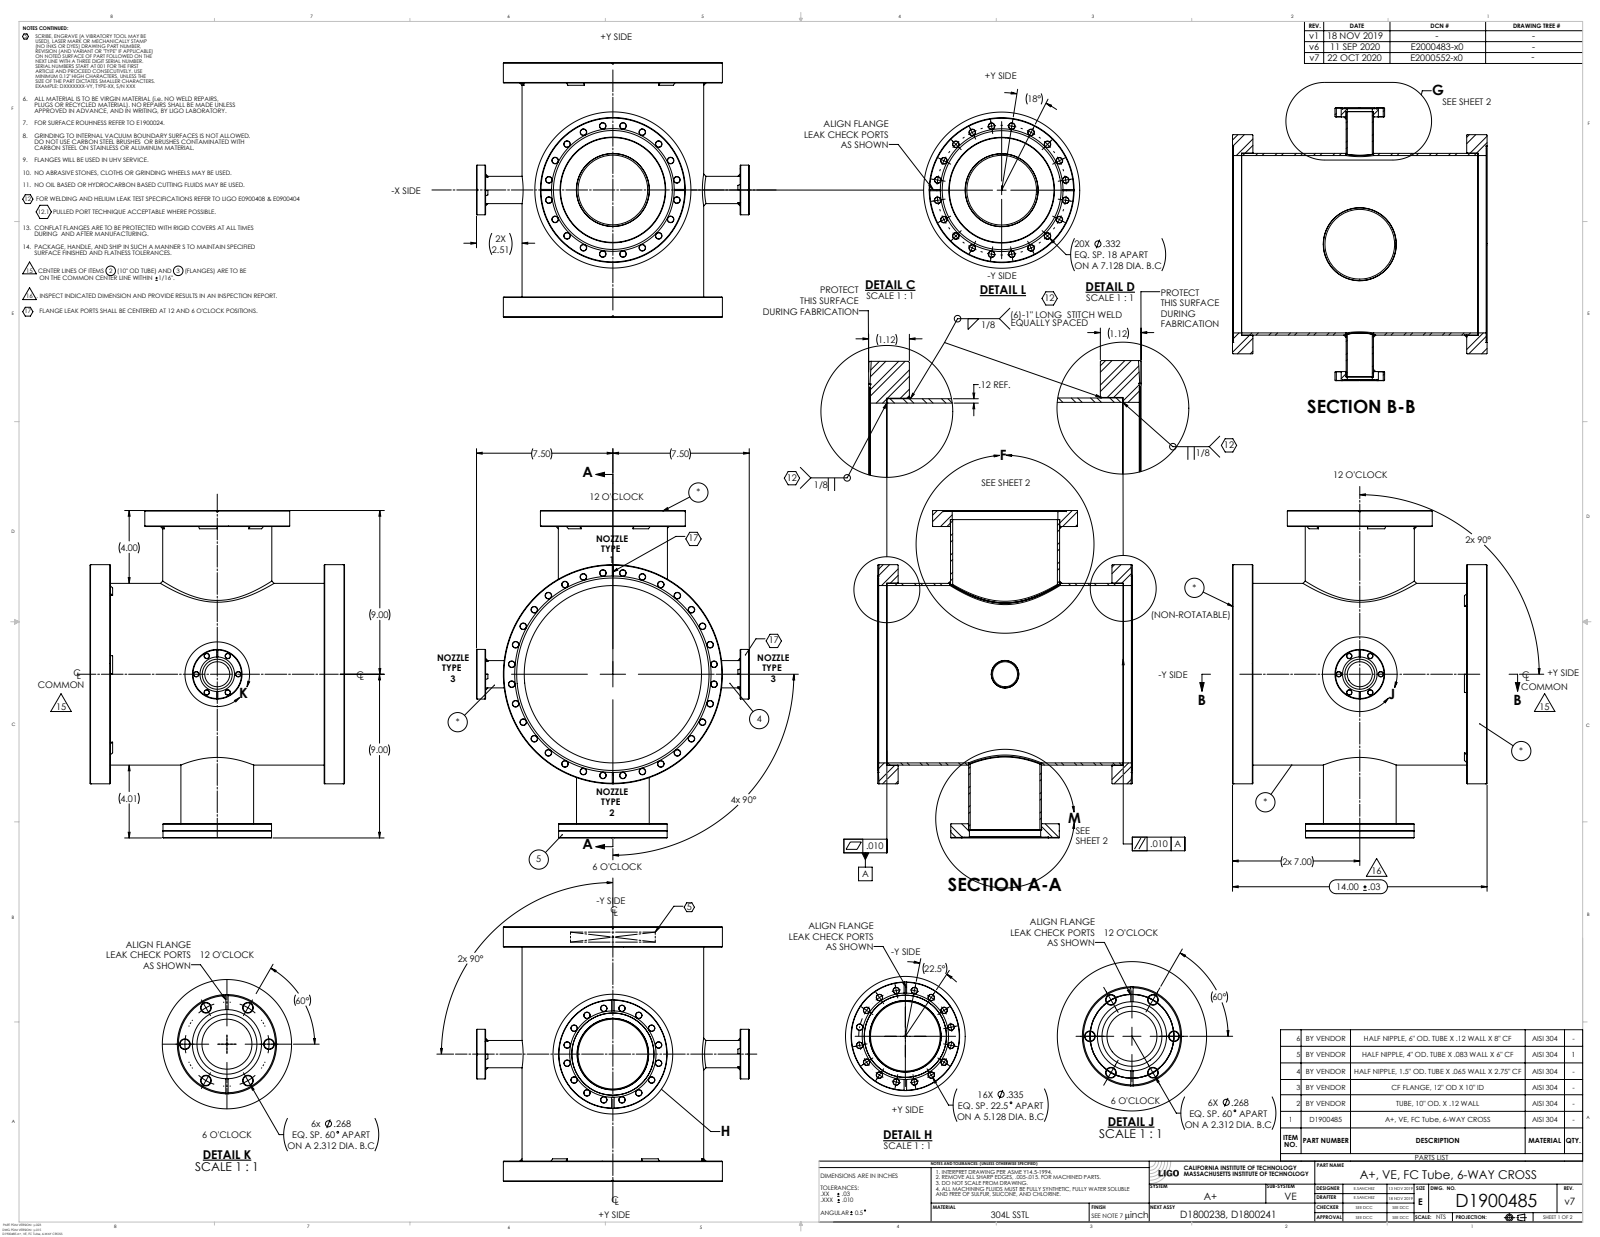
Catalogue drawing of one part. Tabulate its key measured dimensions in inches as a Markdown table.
| quantity | value |
| --- | --- |
| part name | D1900485-v7 |
| STEP written by | SolidWorks 2020 (AUTOMOTIVE_DESIGN) |
| units | inches |
| bodies | 133 solids, 4355 faces (1283 planar, 1674 cylindrical, 1398 other) |
| overall size | 31.363 × 25.625 × 23.503 |
| volume | 420.4 in³ |
| surface area | 4 081 in² |
| round holes (diameter × count) | 0.332 × 52, 0.268 × 30, 0.26 × 24, 0.281 × 20, 0.354 × 20, 0.197 × 18, 0.555 × 17, 0.13 × 16, 0.252 × 16, 0.272 × 16, 0.335 × 16, 0.059 × 12 |
| round bosses / shafts (diameter × count) | 0.236 × 4, 2.73 × 3, 1.98 × 3, 1.896 × 3, 1.772 × 3, 1.734 × 3, 2.677 × 2, 2.421 × 2 |
| partial cylindrical surfaces (radius × count) | 0.075 × 24, 0.033 × 20, 0.169 × 12, 0.197 × 12, 0.008 × 4, 0.079 × 4, 0.091 × 4, 0.118 × 4 |
| main face-to-face distances | 0.118, 0.945, 20.747, 0.944, 19.803, 20.748, 21.692, 1.063, 1.062, 20.865 |
| hole center spacings | 4.279, 9.861, 8.643, 6.212, 7.093, 9.296, 10.966, 2.203 |
